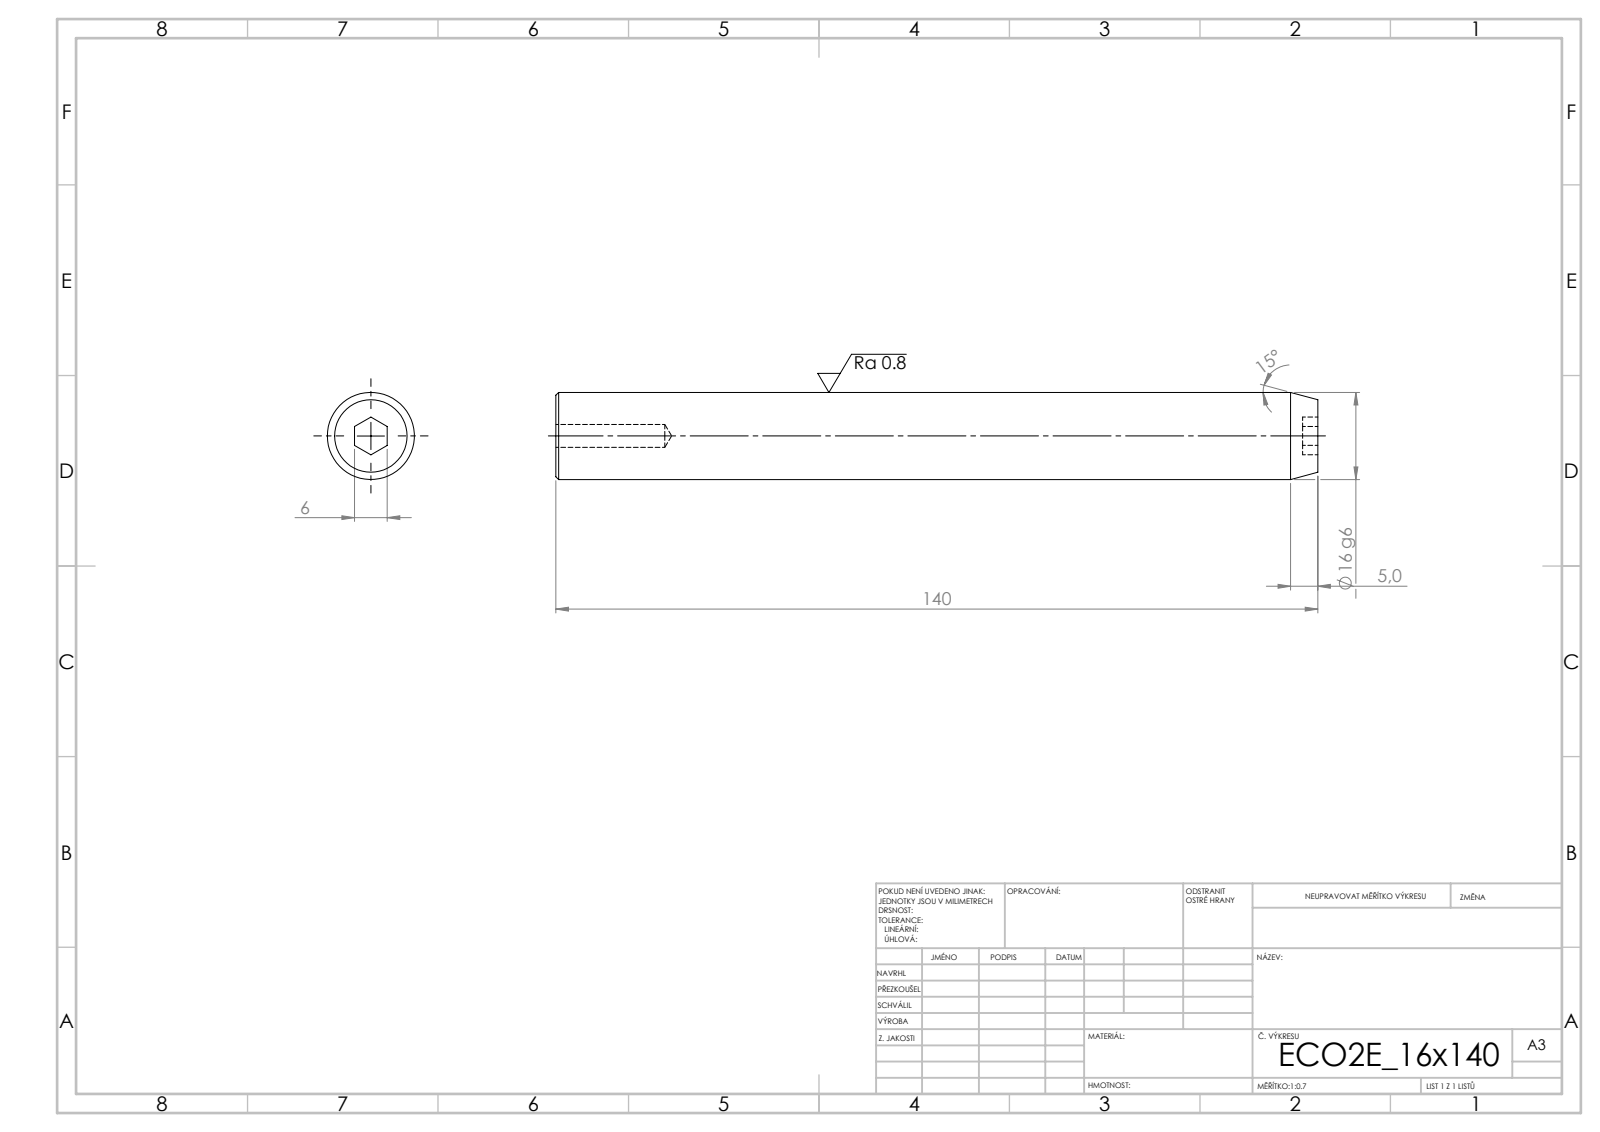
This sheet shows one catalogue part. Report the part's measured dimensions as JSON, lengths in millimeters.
{"step_written_by": "SolidWorks 2019 (CONFIG_CONTROL_DESIGN)", "units": "millimeters", "bodies": {"solids": 1, "faces": 19, "planar": 9, "cylindrical": 4, "other": 6}, "overall_size": [140, 16, 16], "volume_mm3": 27613, "surface_area_mm2": 7674, "round_holes": [[4.2, 1]], "round_bosses_or_shafts": [[16, 1]], "face_to_face_distances": [140, 2.8, 137.2, 6]}
